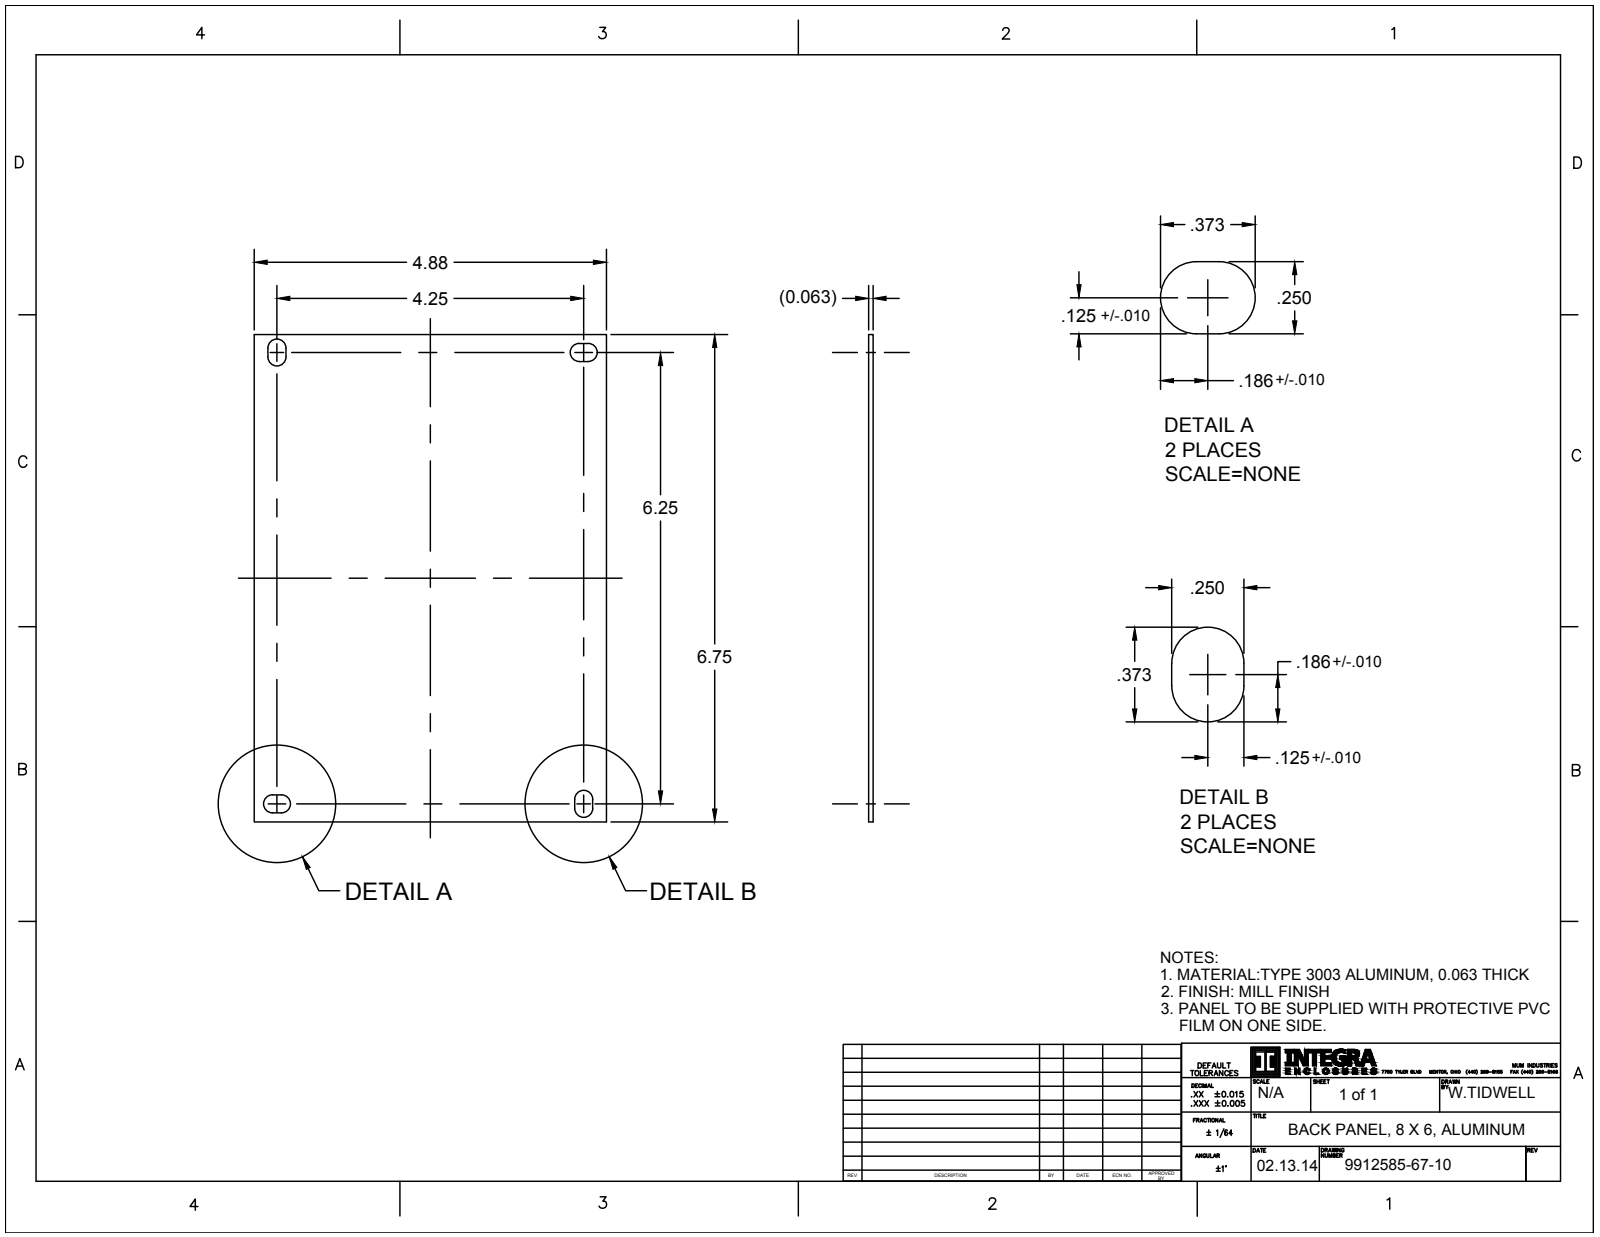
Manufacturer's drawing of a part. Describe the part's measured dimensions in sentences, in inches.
The part is named "9912585-67-10; 9912518-82-10; ABP86_ASM". Its 3-D file was written by "CREO PARAMETRIC BY PTC INC, 2016050 (CONFIG_CONTROL_DESIGN)". It is 5 solids with 430 faces: 90 planar, 268 cylindrical and 72 other. Overall it measures 6.75 by 4.88 by 0.443 inches. Its volume is 2.123 cubic inches and its surface area 69.49 square inches. Round bosses or shafts: 4 of diameter 0.373, 4 of diameter 0.19, 4 of diameter 0.149. Partial cylindrical surfaces (rounded edges, fillets, slot ends): 48 of radius 0.004, 8 of radius 0.125. The main face-to-face distances are 0.063, 4.88, 6.75, 0.25, 0.313, 0.25, 4.233, 6.225, 0.333, 0.083.
